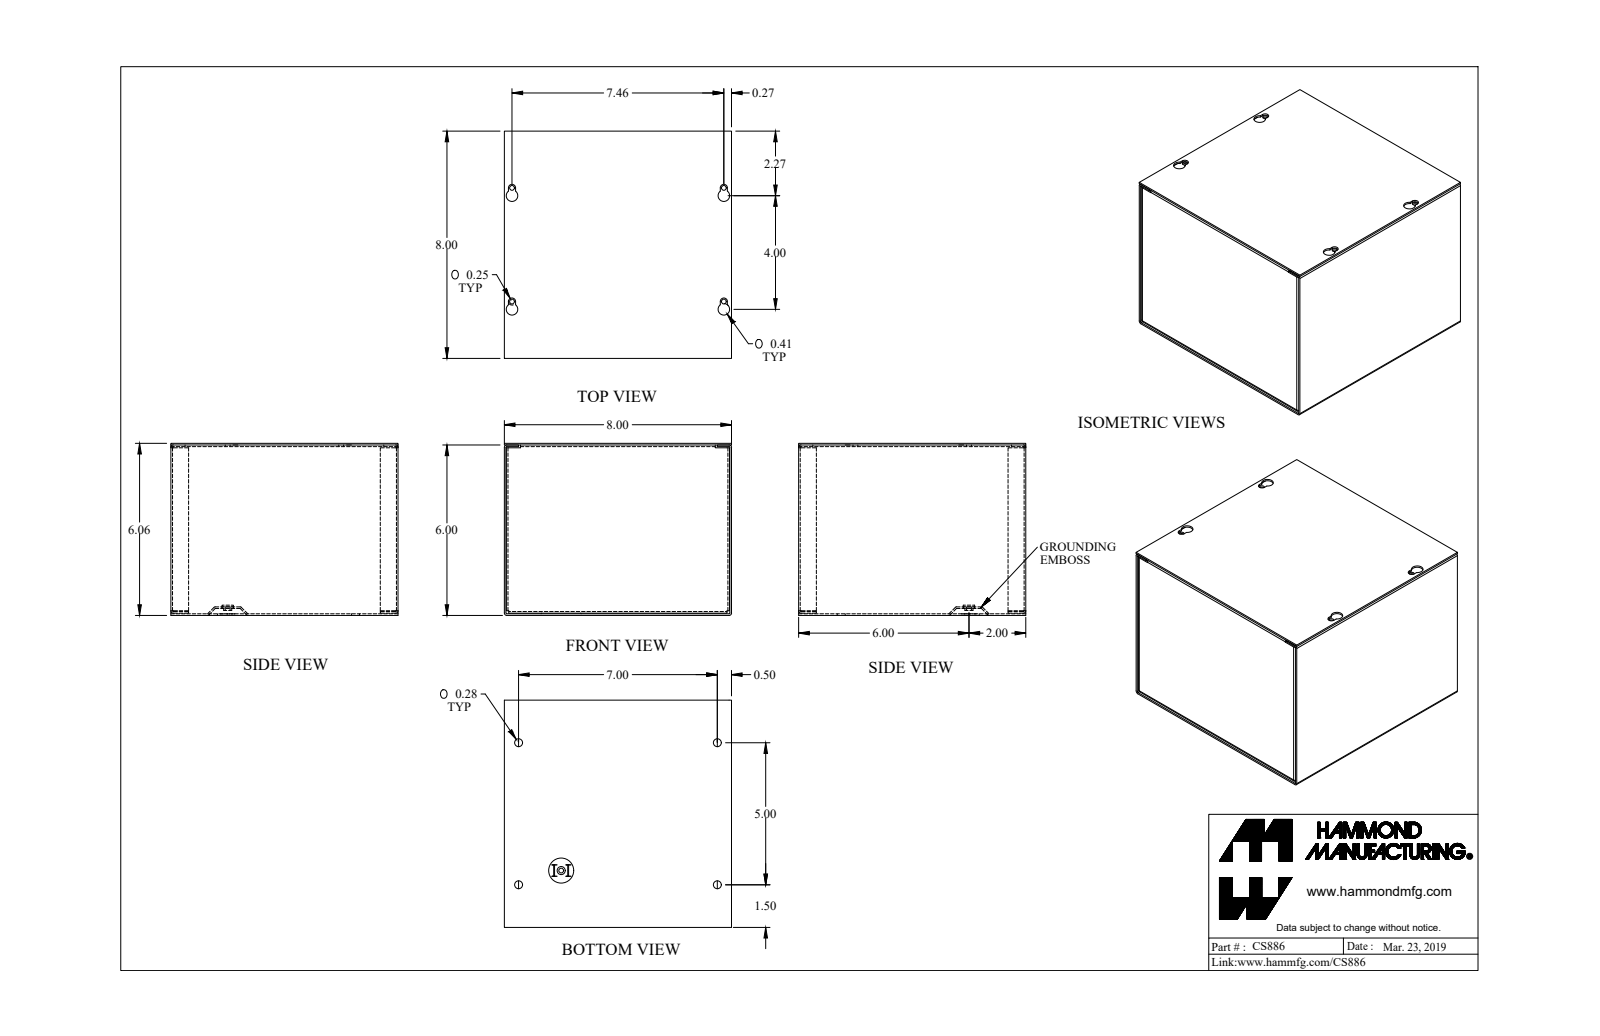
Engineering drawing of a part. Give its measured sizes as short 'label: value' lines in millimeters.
name: CS886_Default
written by: SolidWorks 2019 (CONFIG_CONTROL_DESIGN)
unit: mm
bodies: 4 solids, 205 faces (125 planar, 72 cylindrical, 8 other)
size: 203.2 × 203.2 × 153.8
volume: 325 300 mm³; area: 455 400 mm²
holes: 5× ⌀4.3, 4× ⌀7.1, 1× ⌀12.7
bosses: 1× ⌀12.5, 1× ⌀7.2
rounds: 12× R0.7, 12× R2.2, 8× R1.4, 4× R3.2, 4× R5.2
face distances: 1.4, 201.8, 152.4, 203.2, 200.3, 151, 153.8, 1.8, 200, 2
hole spacings: 14, 114.5, 184.1, 216.3, 101.6, 127, 177.8, 189.5
